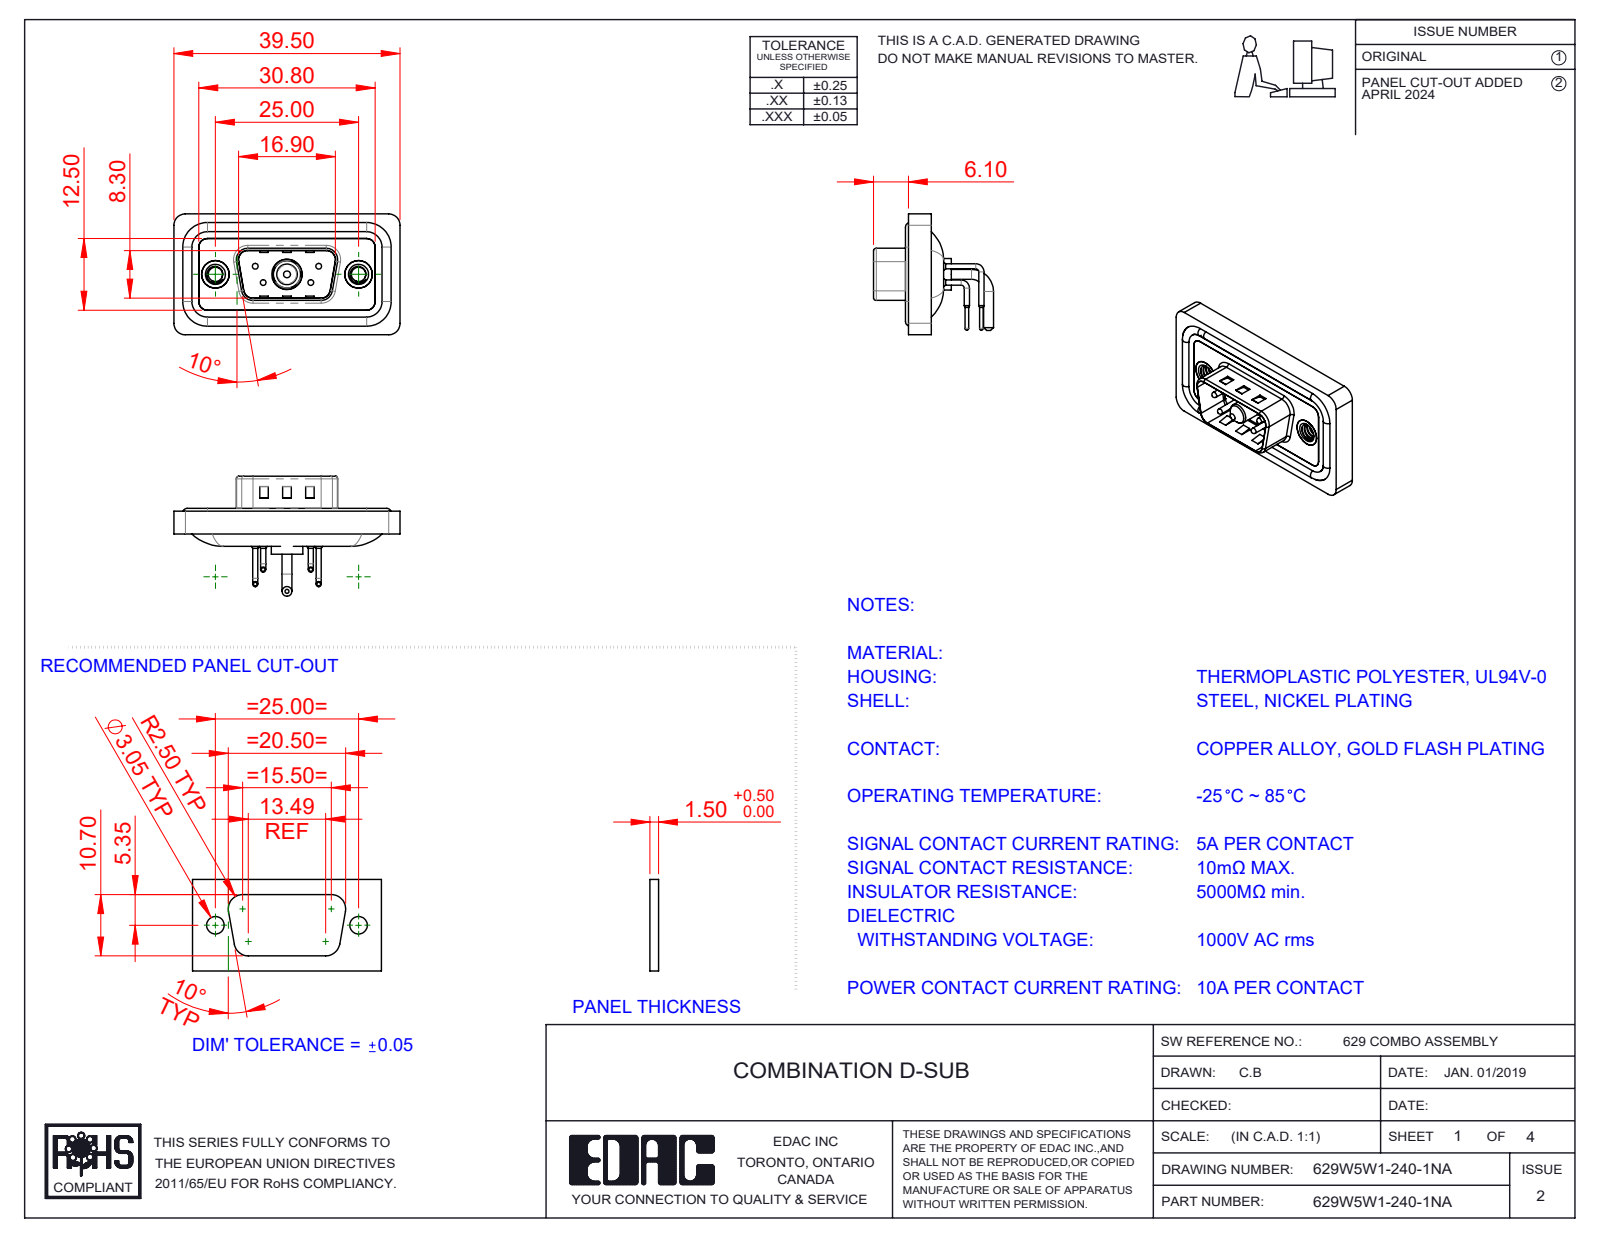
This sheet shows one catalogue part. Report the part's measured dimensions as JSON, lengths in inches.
{"part_name": "629W5W1-240-1NA; 629Combo Shell Front_09 Contacts; 629Combo Contact Row 2; Power Pin_10A RA (+5 more)", "step_written_by": "SolidWorks 2023 (CONFIG_CONTROL_DESIGN)", "units": "inches", "bodies": {"solids": 13, "faces": 888, "planar": 411, "cylindrical": 343, "other": 134}, "overall_size": [1.555, 0.831, 0.825], "volume_in3": 0.27, "surface_area_in2": 11.03, "round_holes": [[0.03, 4], [0.063, 4], [0.079, 4], [0.098, 2], [0.157, 2], [0.189, 2], [0.197, 2], [0.191, 1], [0.209, 1]], "round_bosses_or_shafts": [[0.035, 8], [0.063, 4], [0.059, 4], [0.039, 4], [0.026, 4], [0.193, 2], [0.067, 2], [0.217, 1]], "partial_cylinders_radius": [[0.059, 18], [0.079, 18], [0.02, 8], [0.063, 8], [0.01, 4], [0.024, 4], [0.026, 4], [0.035, 4]], "face_to_face_distances": [0.016, 0.114, 0.043, 0.031, 0.083, 0.098, 0.063, 0.122, 0.059, 0.177], "hole_center_spacings": [0.124, 0.225, 0.28, 0.492, 0.713, 0.173, 0.173, 0.327]}
